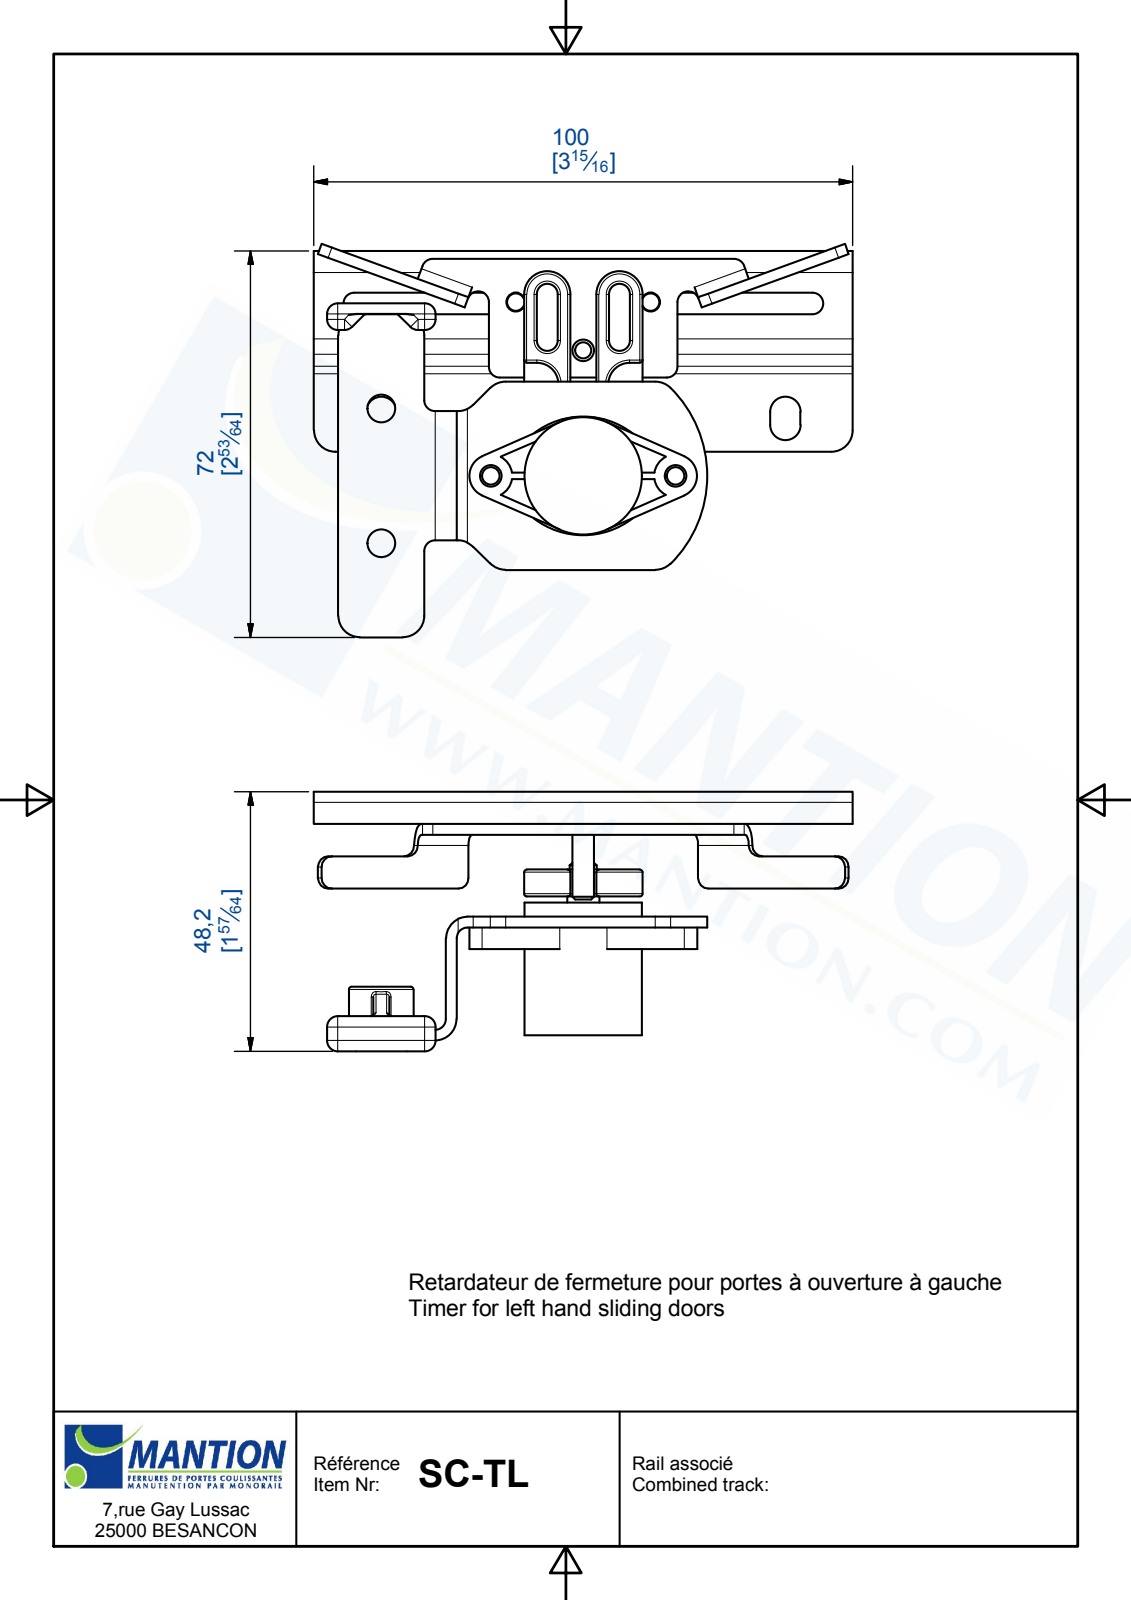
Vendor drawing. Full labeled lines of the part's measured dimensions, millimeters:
Part name (STEP PRODUCT): SC-TL
STEP written by: Autodesk Inventor 2019 (AUTOMOTIVE_DESIGN)
Units: millimetres
Bodies: 2 solids, 512 faces (197 planar, 175 cylindrical, 140 other)
Overall size (bounding box): 100 × 73.06 × 48.2
Volume: 30 643 mm³ · Surface area: 24 596 mm²
Round holes (diameter × count): ⌀3.24 ×4, ⌀3.5 ×2, ⌀4 ×2, ⌀5.2 ×2
Round bosses / shafts (diameter × count): ⌀12 ×2, ⌀21.8 ×1, ⌀10 ×1, ⌀6 ×1, ⌀5 ×1, ⌀4 ×1, ⌀1.29 ×1
Partial cylindrical surfaces — rounded edges, fillets, slot ends (radius × count): R2 ×48, R0.5 ×32, R4 ×27, R0.2 ×6, R1.95 ×4, R2.8 ×4, R0.49 ×2, R4.3 ×2
Main face-to-face distances: 2, 4, 6, 23.2, 17.2, 21.2, 8, 44.2, 40.2, 21
Hole centre spacings: 23.88, 25, 32.59, 43.82, 56.06, 31.87, 34.3, 51.27
